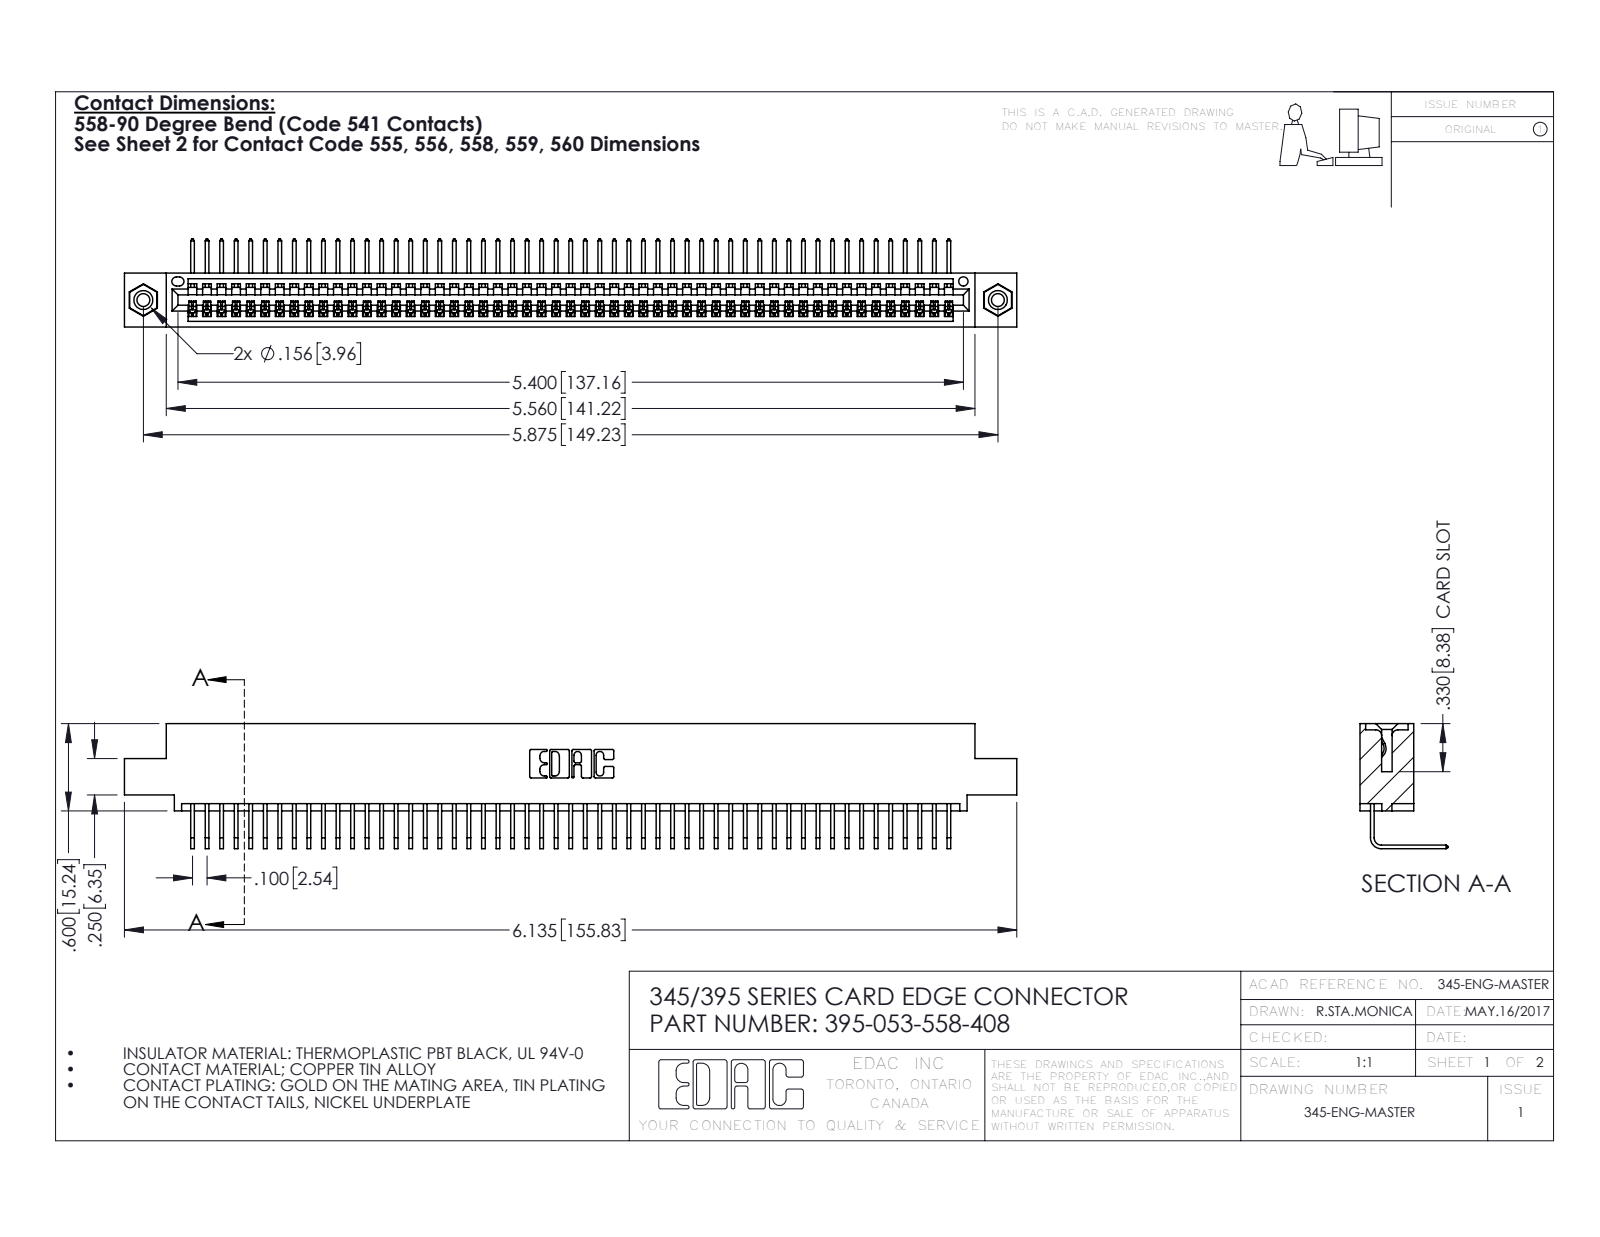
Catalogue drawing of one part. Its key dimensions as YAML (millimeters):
part_name: "345-292-001_558 Tail - 2; 345 Part_0.110 Offset - 0.156 Dia-TI; 395-053-558-408; 345-250-001_345-250-003-102"
step_written_by: "SolidWorks 2016 (CONFIG_CONTROL_DESIGN)"
units: millimeters
bodies: {solids: 56, faces: 3370, planar: 2342, cylindrical: 1012, other: 16}
overall_size: [155.8, 21.8, 15.4]
volume: 15000
surface_area: 21210
round_holes:
  - {diameter: 2.3, count: 2}
  - {diameter: 3.2, count: 2}
  - {diameter: 4, count: 2}
  - {diameter: 1.6, count: 1}
round_bosses_or_shafts:
  - {diameter: 3.9, count: 2}
partial_cylinders:
  - {radius: 0.2, count: 106}
  - {radius: 0.3, count: 22}
  - {radius: 0.2, count: 6}
  - {radius: 0.8, count: 6}
  - {radius: 0.7, count: 3}
  - {radius: 0.8, count: 2}
  - {radius: 1, count: 2}
  - {radius: 0.4, count: 1}
face_to_face_distances: [1.8, 7.6, 9.4, 5.1, 2.5, 6.9, 0.6, 5.7, 3.8, 1.8]
hole_center_spacings: [6.9, 143.2, 149.2]
